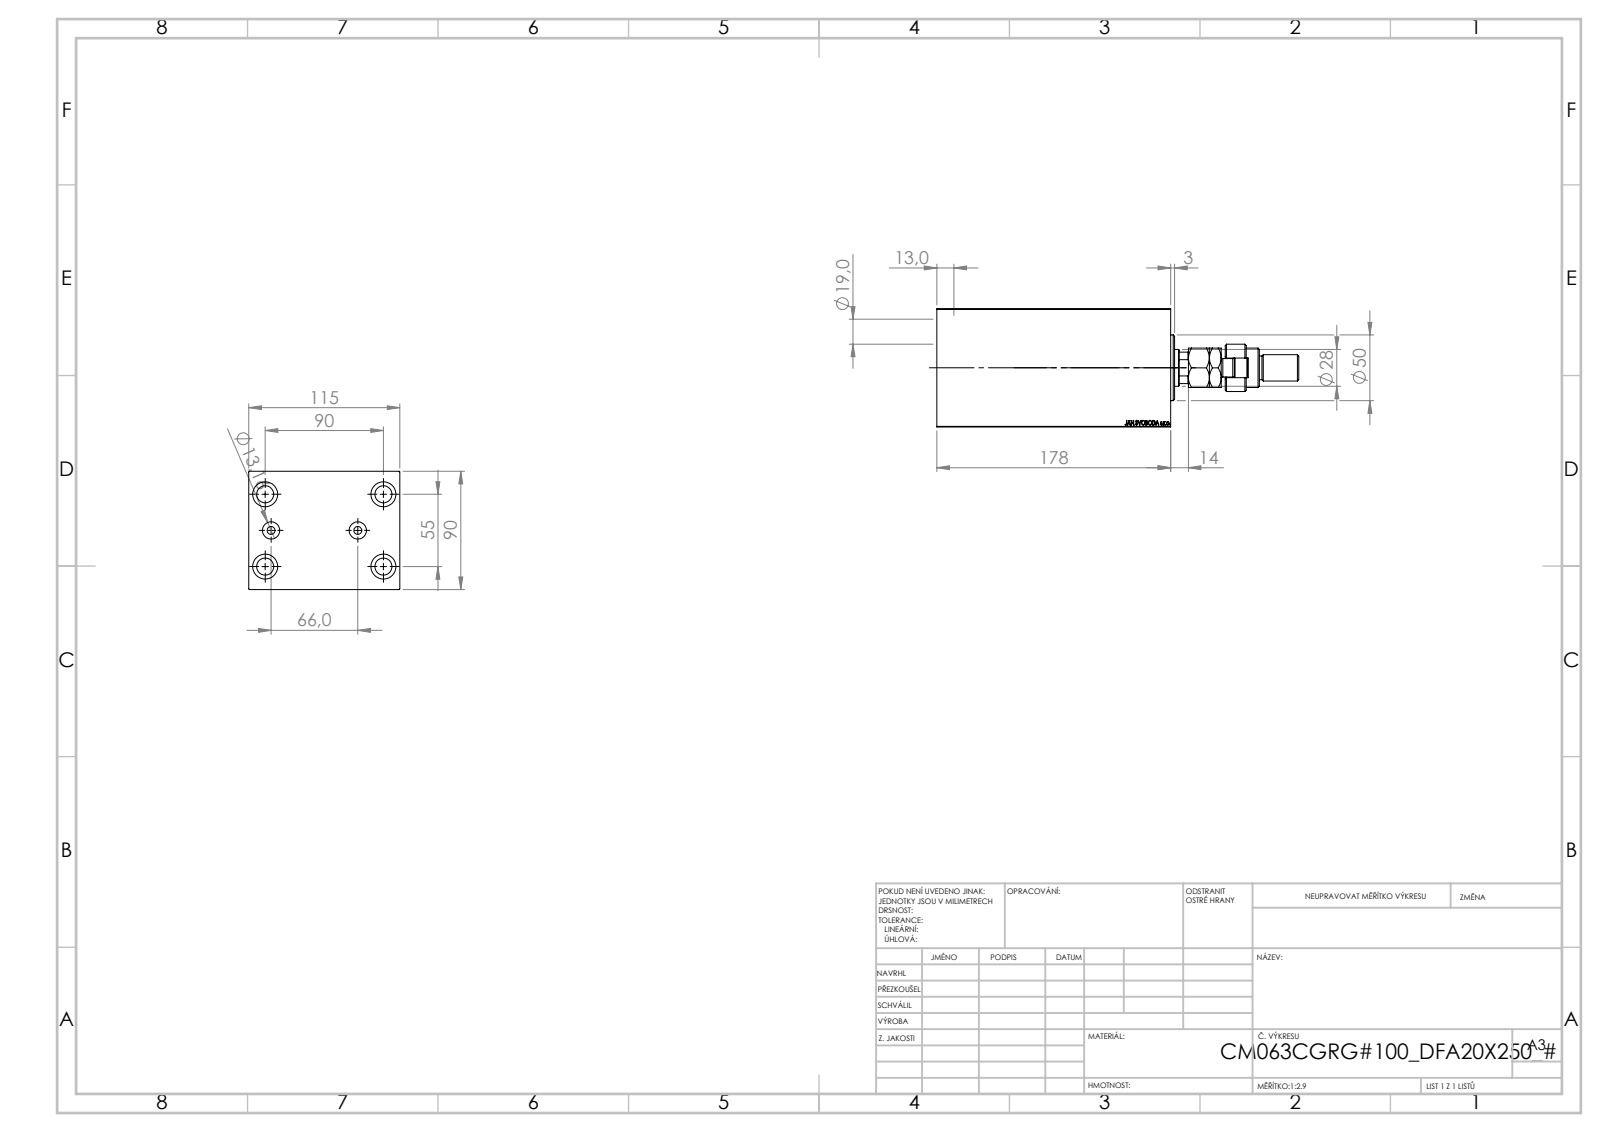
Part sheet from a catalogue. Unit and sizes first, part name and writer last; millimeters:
Units: millimetres
Overall size (bounding box): 275.5 × 115 × 90
Round holes (diameter × count): ⌀13 ×4, ⌀19 ×4, ⌀6 ×2, ⌀13.16 ×2, ⌀18.5 ×1, ⌀28 ×1, ⌀31.5 ×1, ⌀63 ×1, ⌀65 ×1, ⌀72 ×1
Round bosses / shafts (diameter × count): ⌀50 ×1, ⌀36 ×1, ⌀30 ×1, ⌀22 ×1, ⌀20 ×1, ⌀18 ×1, ⌀14 ×1
Partial cylindrical surfaces — rounded edges, fillets, slot ends (radius × count): R7.5 ×1, R12 ×1, R13.5 ×1
Main face-to-face distances: 90, 115, 178, 46, 132, 10, 168, 5, 122, 3
Hole centre spacings: 30, 52.74, 82.71, 33, 55, 90, 105.48, 66
Volume: 1 524 000 mm³ · Surface area: 200 486 mm²
Bodies: 5 solids, 946 faces (437 planar, 71 cylindrical, 438 other)
Part name (STEP PRODUCT): V450CM_VC_B; V450CM_C_Body; V450CM_C_VCP; MFA (+1 more)
STEP written by: SolidWorks 2019 (CONFIG_CONTROL_DESIGN)
